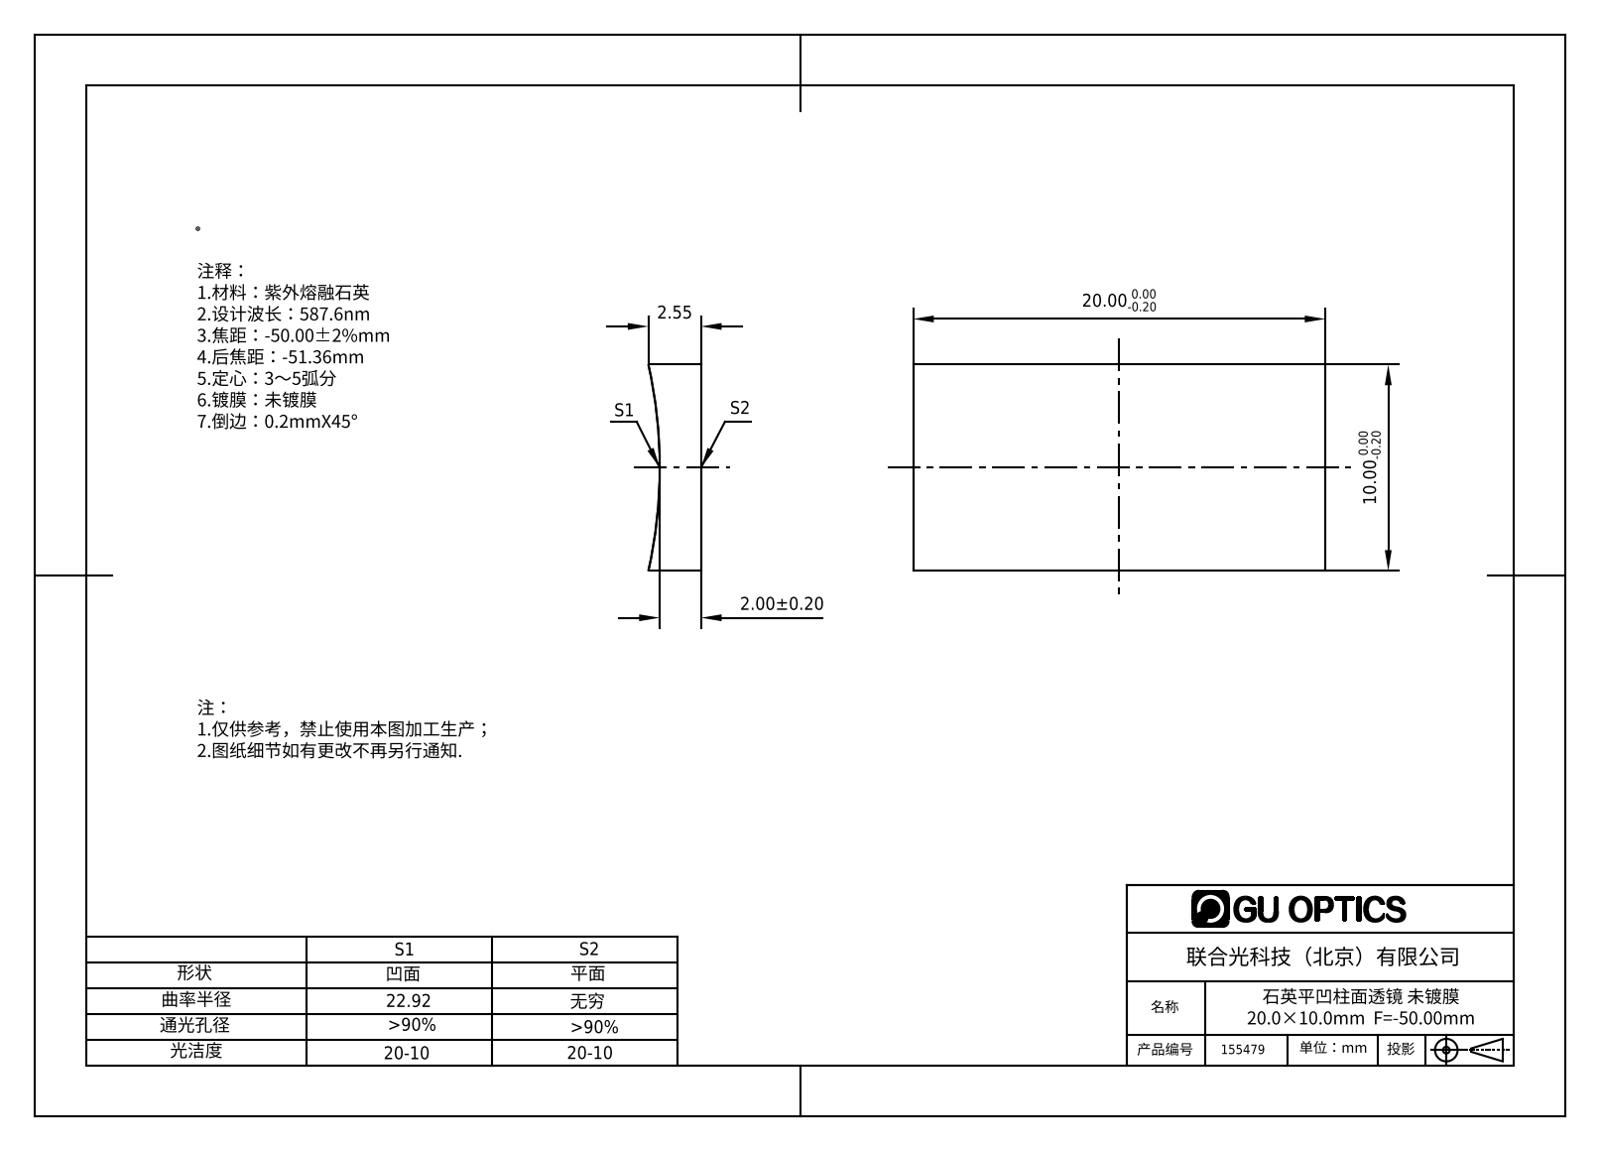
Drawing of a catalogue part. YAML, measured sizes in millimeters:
part_name: "155479"
step_written_by: "SolidWorks 2016 (AUTOMOTIVE_DESIGN)"
units: millimeters
bodies: {solids: 1, faces: 6, planar: 5, cylindrical: 1, other: 0}
overall_size: [20, 10, 2.55]
volume: 437
surface_area: 547
partial_cylinders:
  - {radius: 22.92, count: 1}
face_to_face_distances: [10, 20]
